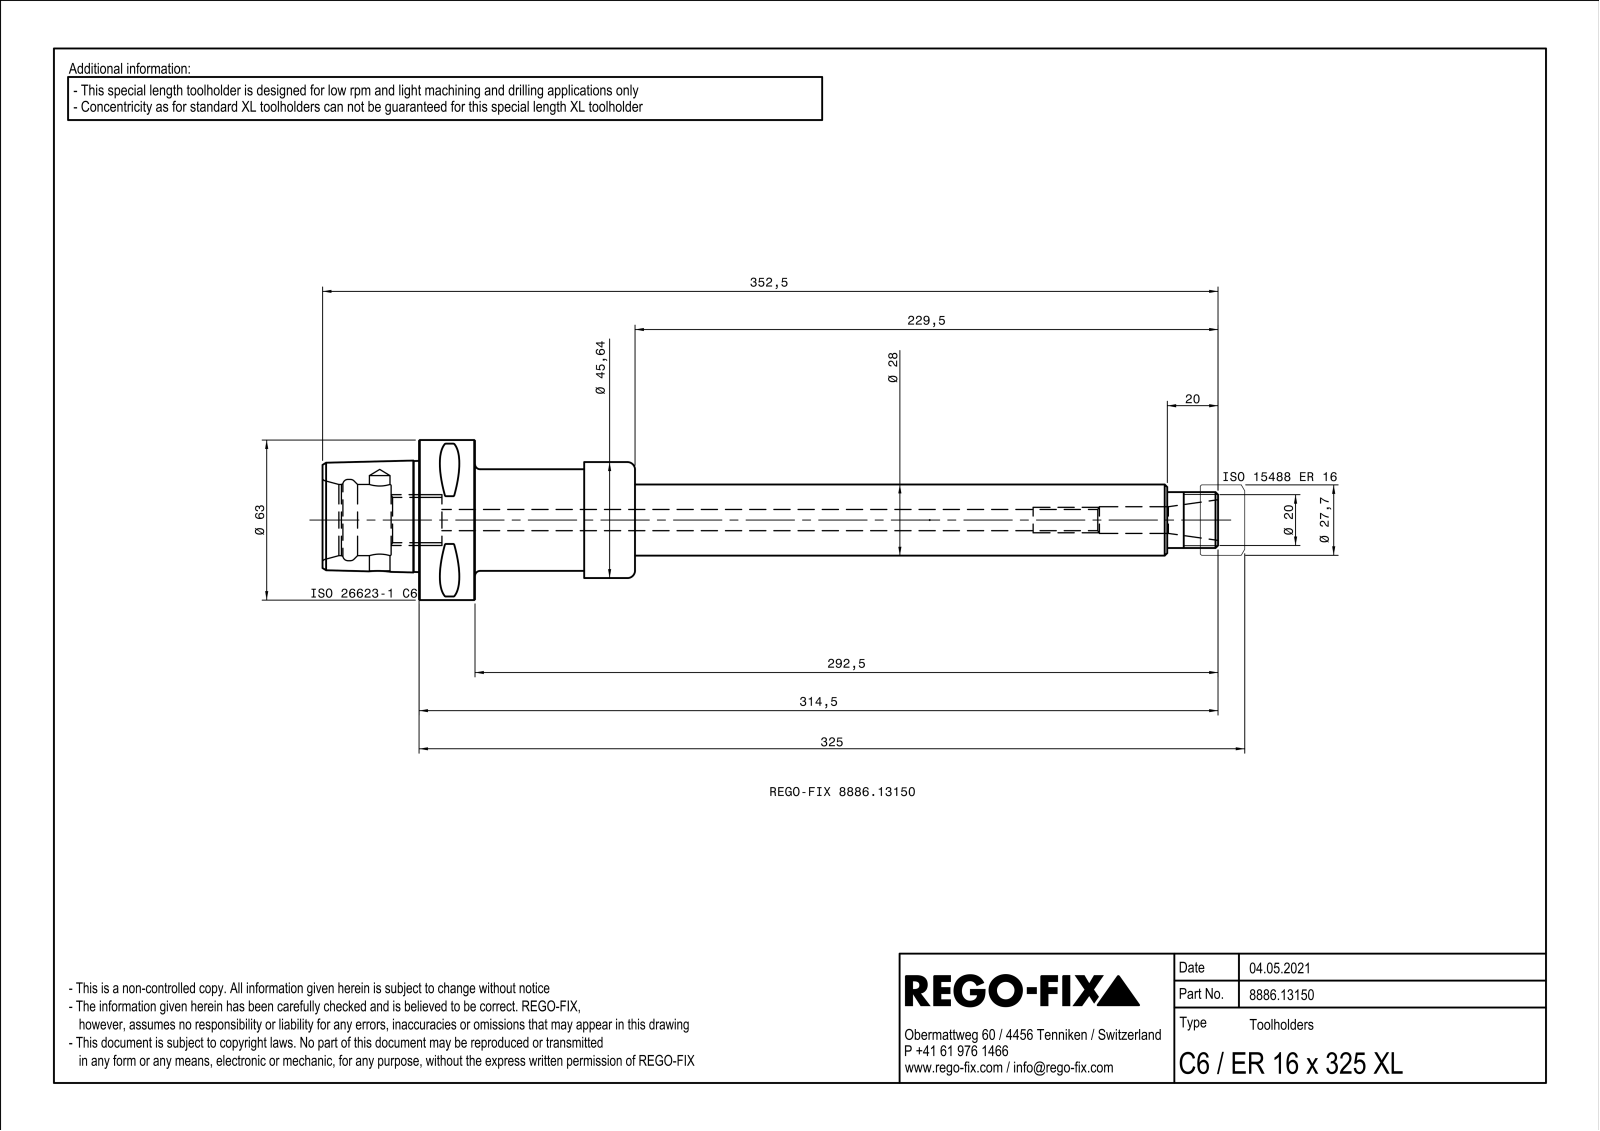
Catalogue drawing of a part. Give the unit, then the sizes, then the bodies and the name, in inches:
Units: inches
Overall size (bounding box): 13.878 × 2.48 × 2.48
Round holes (diameter × count): ⌀0.157 ×1, ⌀0.319 ×1, ⌀0.329 ×1, ⌀0.33 ×1, ⌀0.394 ×1, ⌀0.413 ×1, ⌀0.702 ×1, ⌀0.984 ×1, ⌀1.102 ×1, ⌀1.142 ×1, ⌀1.26 ×1, ⌀1.511 ×1
Round bosses / shafts (diameter × count): ⌀2.48 ×1, ⌀1.797 ×1, ⌀1.575 ×1, ⌀1.339 ×1, ⌀1.299 ×1, ⌀0.972 ×1, ⌀0.937 ×1, ⌀0.866 ×1
Partial cylindrical surfaces — rounded edges, fillets, slot ends (radius × count): R0.02 ×8
Main face-to-face distances: 0.866, 2.48, 3.346, 0.177, 2.244, 0.236, 0.551, 4.843, 2.362, 1.496
Hole centre spacings: 1.083
Volume: 17.71 in³ · Surface area: 99.19 in²
Bodies: 1 solid, 156 faces (31 planar, 33 cylindrical, 92 other)
Part name (STEP PRODUCT): NOCUT
STEP written by: SIEMENS PLM Software Solid Edge ST10 (AUTOMOTIVE_DESIGN)
